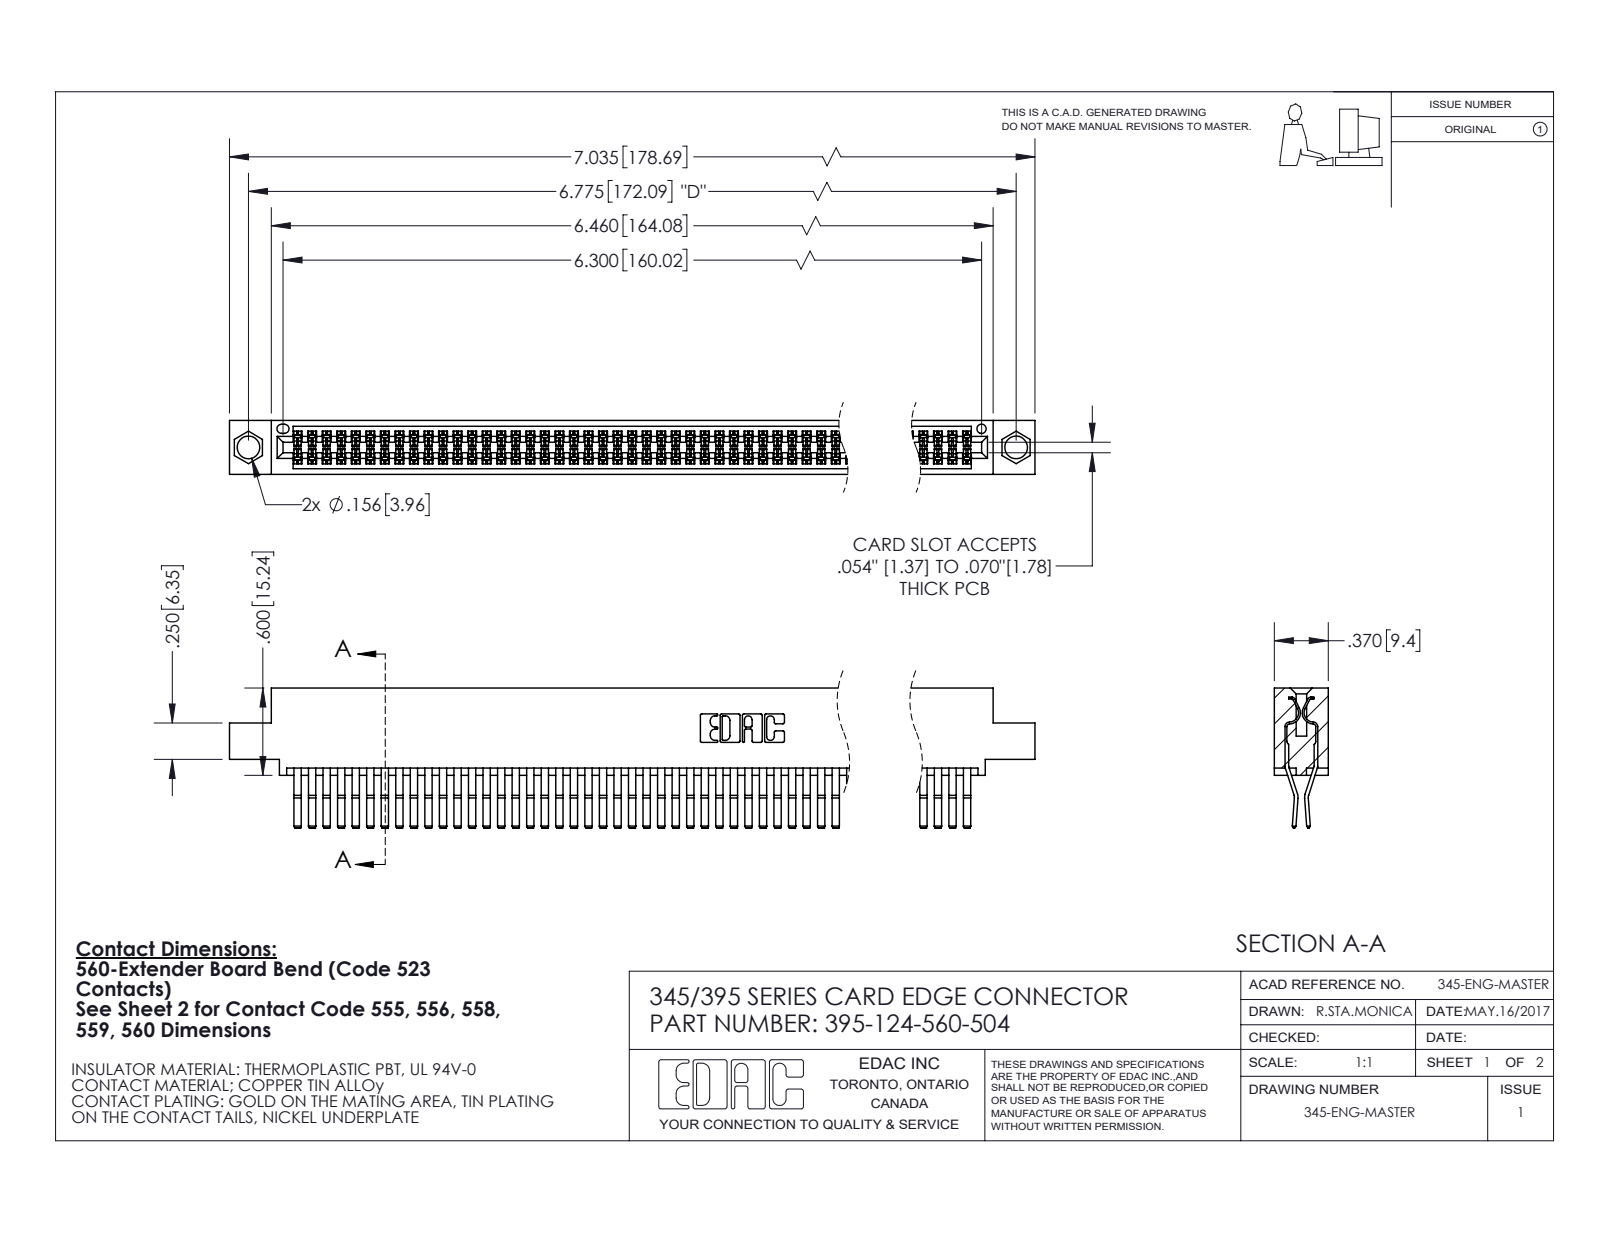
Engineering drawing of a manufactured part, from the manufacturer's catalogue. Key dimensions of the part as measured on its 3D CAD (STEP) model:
Part name (STEP PRODUCT): 395-124-560-504; 345 Part_0.110 Offset - 0.156 Dia-TI; 345-292-001_560 Tail
STEP written by: SolidWorks 2020 (CONFIG_CONTROL_DESIGN)
Units: inches
Bodies: 125 solids, 6592 faces (4190 planar, 2402 cylindrical, 0 other)
Overall size (bounding box): 7.035 × 0.962 × 0.37
Volume: 1.109 in³ · Surface area: 45.4 in²
Round holes (diameter × count): ⌀0.156 ×2, ⌀0.064 ×1
Partial cylindrical surfaces — rounded edges, fillets, slot ends (radius × count): R0.006 ×186, R0.01 ×22, R0.007 ×6, R0.031 ×6, R0.026 ×3, R0.01 ×2, R0.014 ×2, R0.019 ×2
Main face-to-face distances: 0.025, 0.298, 0.072, 0.37, 0.2, 0.098, 0.272, 0.225, 0.175, 0.149
Hole centre spacings: 0.27, 6.539, 6.775
